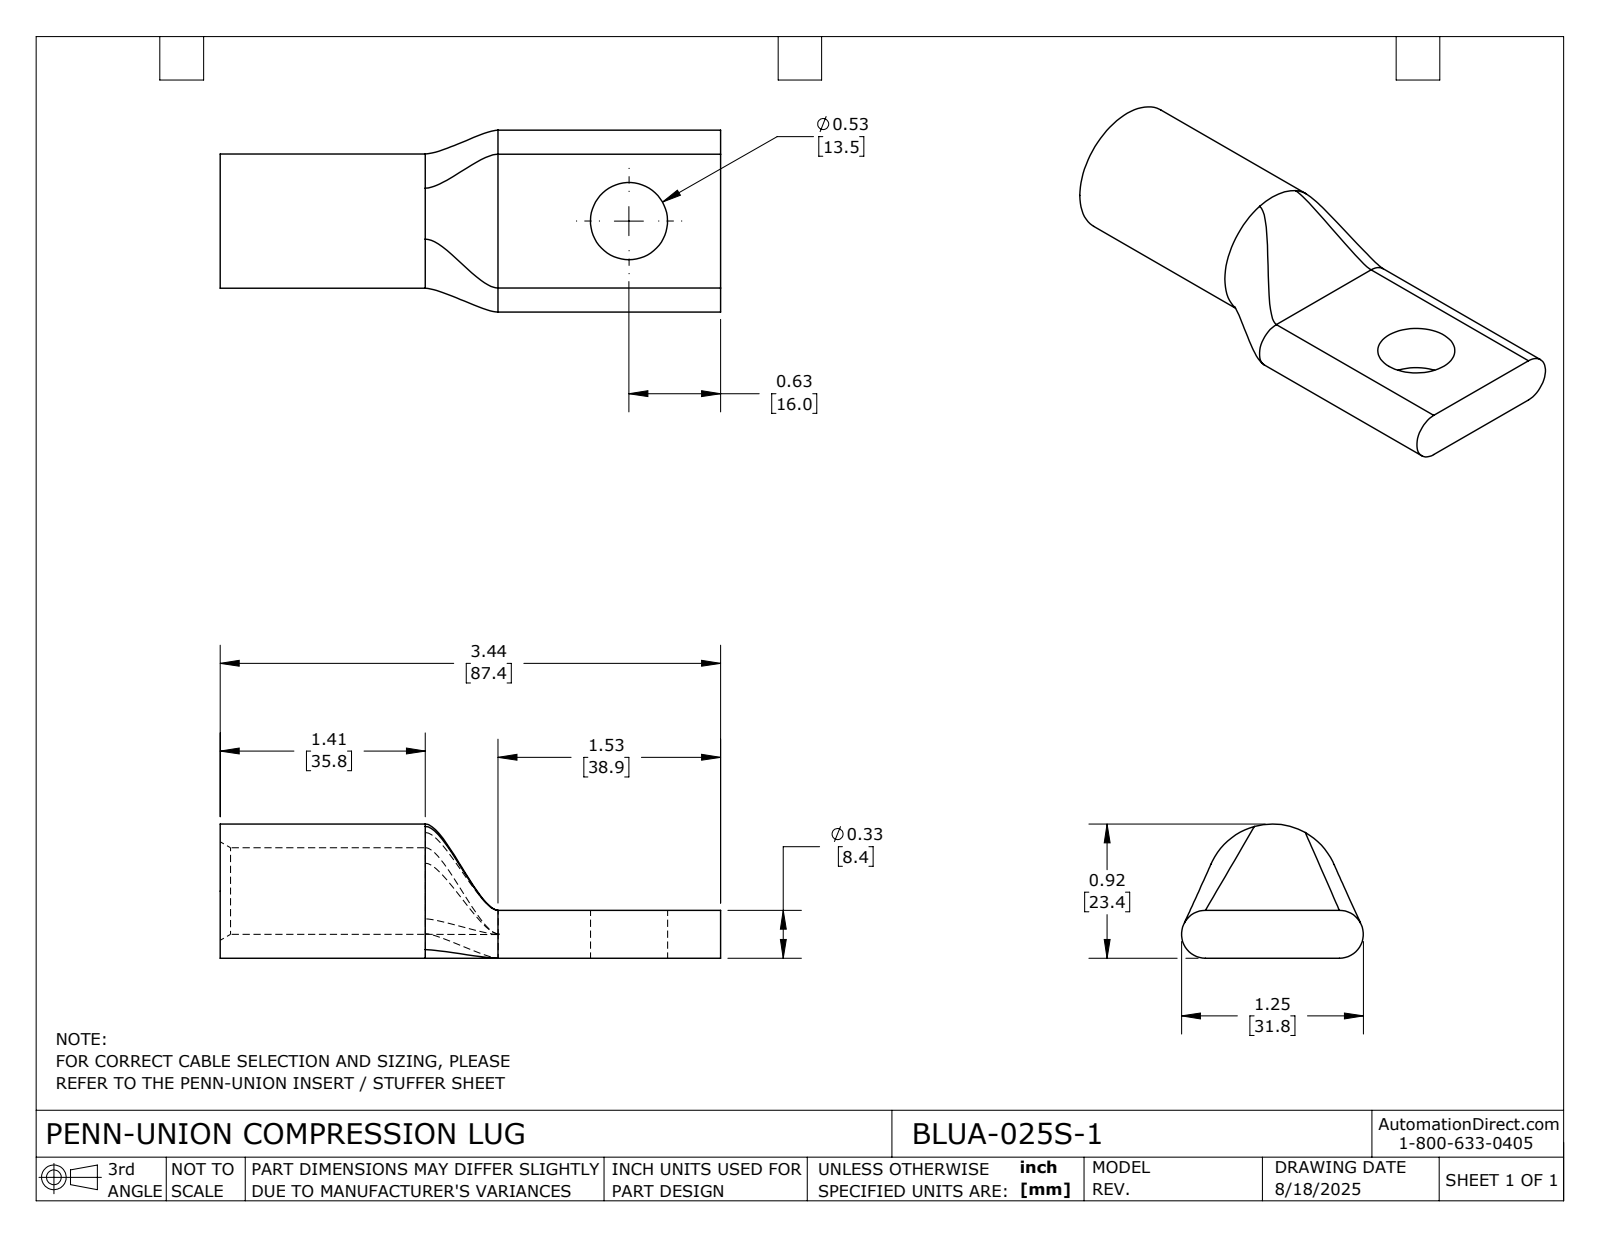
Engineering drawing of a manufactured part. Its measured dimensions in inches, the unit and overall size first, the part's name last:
Units: inches
Overall size (bounding box): 3.44 × 1.25 × 0.923
Round holes (diameter × count): ⌀0.53 ×1, ⌀0.595 ×1
Round bosses / shafts (diameter × count): ⌀0.923 ×1
Partial cylindrical surfaces — rounded edges, fillets, slot ends (radius × count): R0.165 ×2
Main face-to-face distances: 0.33, 3.44, 1.91, 1.53
Volume: 1.265 in³ · Surface area: 14.76 in²
Bodies: 1 solid, 24 faces (5 planar, 9 cylindrical, 10 other)
Part name (STEP PRODUCT): BLUA-025S-1
STEP written by: SolidWorks 2024 (CONFIG_CONTROL_DESIGN)
